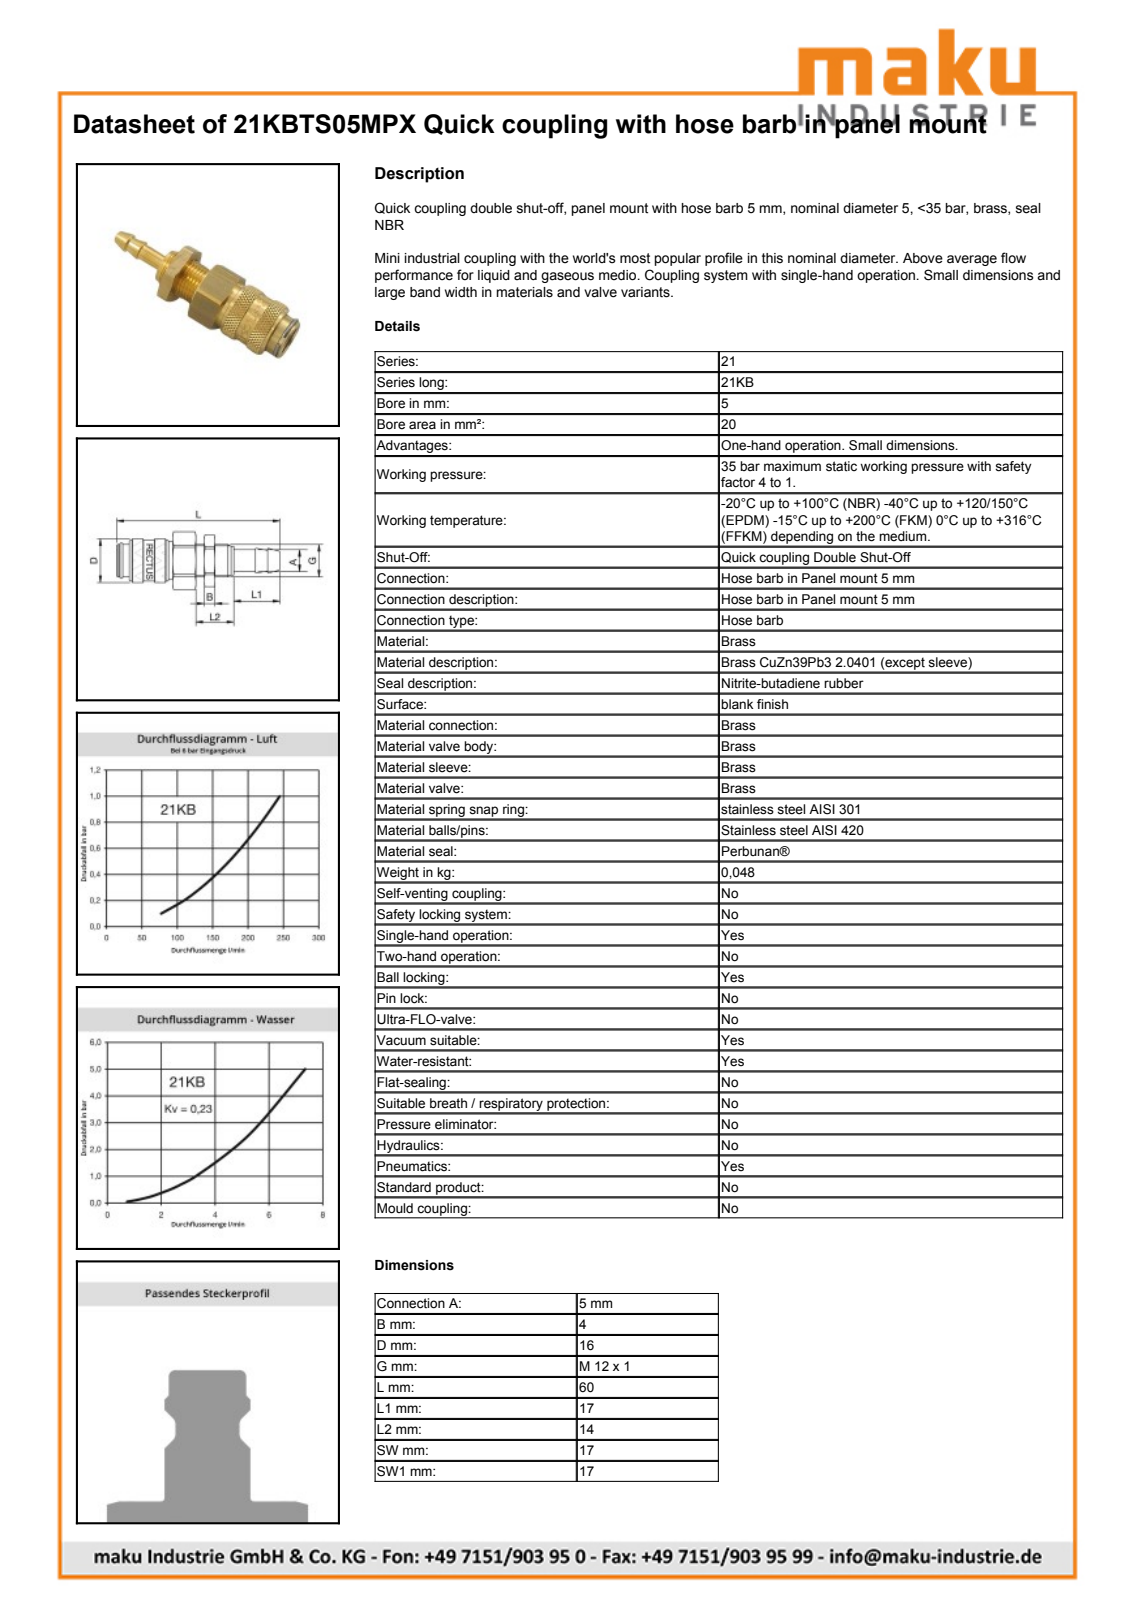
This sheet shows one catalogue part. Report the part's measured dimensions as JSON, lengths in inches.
{"part_name": "21KATS05MPN", "step_written_by": "Autodesk Inventor 2019 (CONFIG_CONTROL_DESIGN)", "units": "inches", "bodies": {"solids": 2, "faces": 498, "planar": 161, "cylindrical": 71, "other": 266}, "overall_size": [2.38, 0.754, 0.754], "volume_in3": 0.476, "surface_area_in2": 7.277, "round_holes": [[0.478, 1], [0.551, 1]], "round_bosses_or_shafts": [[0.636, 1], [0.594, 1], [0.472, 1], [0.449, 1], [0.439, 1], [0.426, 1], [0.417, 1], [0.199, 1]], "partial_cylinders_radius": [[0.293, 1], [0.377, 1]], "face_to_face_distances": [0.669, 1.159, 1.338, 0.179, 1.496, 0.336, 0.157, 0.823, 0.337, 0.515]}
